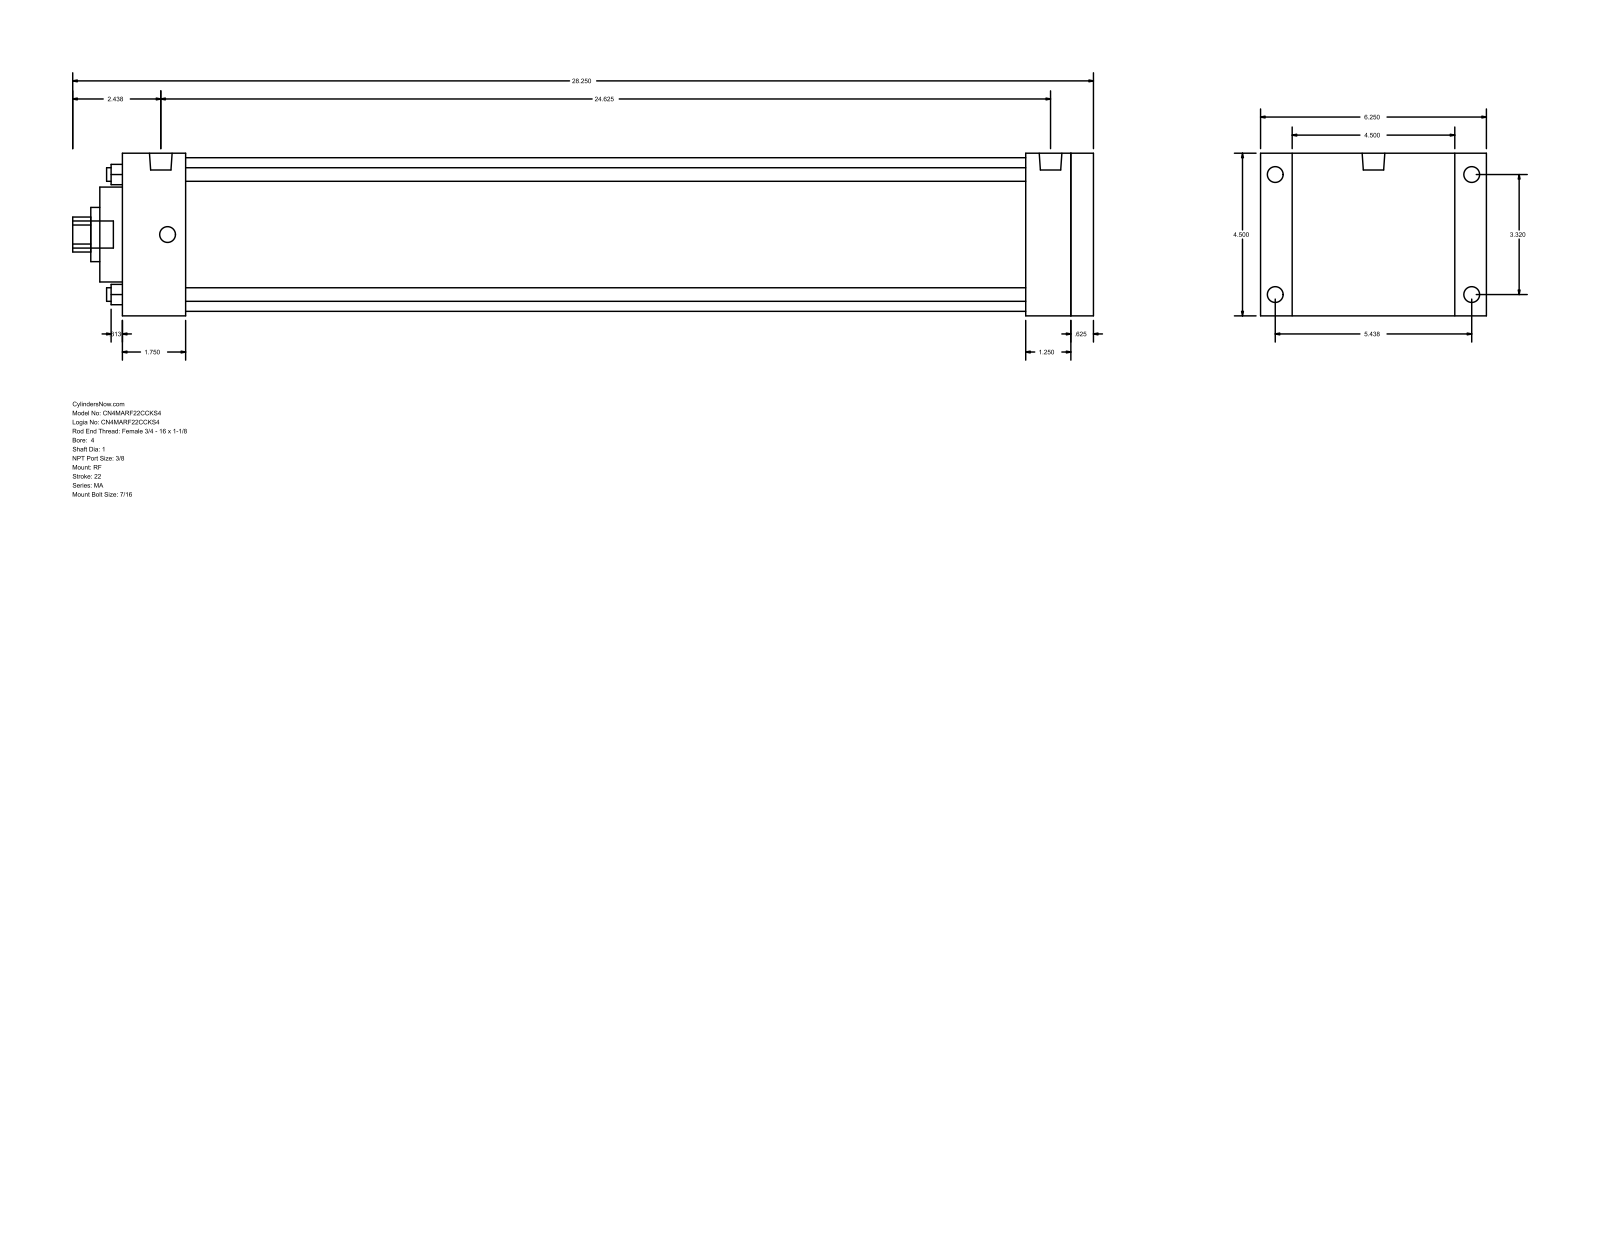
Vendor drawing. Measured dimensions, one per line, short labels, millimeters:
name: MA_RF__0400_1
written by: GSSL Pune (CONFIG_CONTROL_DESIGN)
unit: mm
bodies: 0 solids, 94 faces (65 planar, 29 cylindrical, 0 other)
size: 717.55 × 158.75 × 114.3
holes: 4× ⌀9.53, 1× ⌀25.4, 1× ⌀38.1, 1× ⌀66.67, 1× ⌀107.95
bosses: 8× ⌀11.11, 2× ⌀15.93, 1× ⌀19.05
rounds: 1× R12.29
face distances: 114.3, 682.63, 666.75, 15.88, 22.23, 136.53, 635, 31.75, 47.63, 44.46
hole spacings: 59.62, 84.32, 119.25
